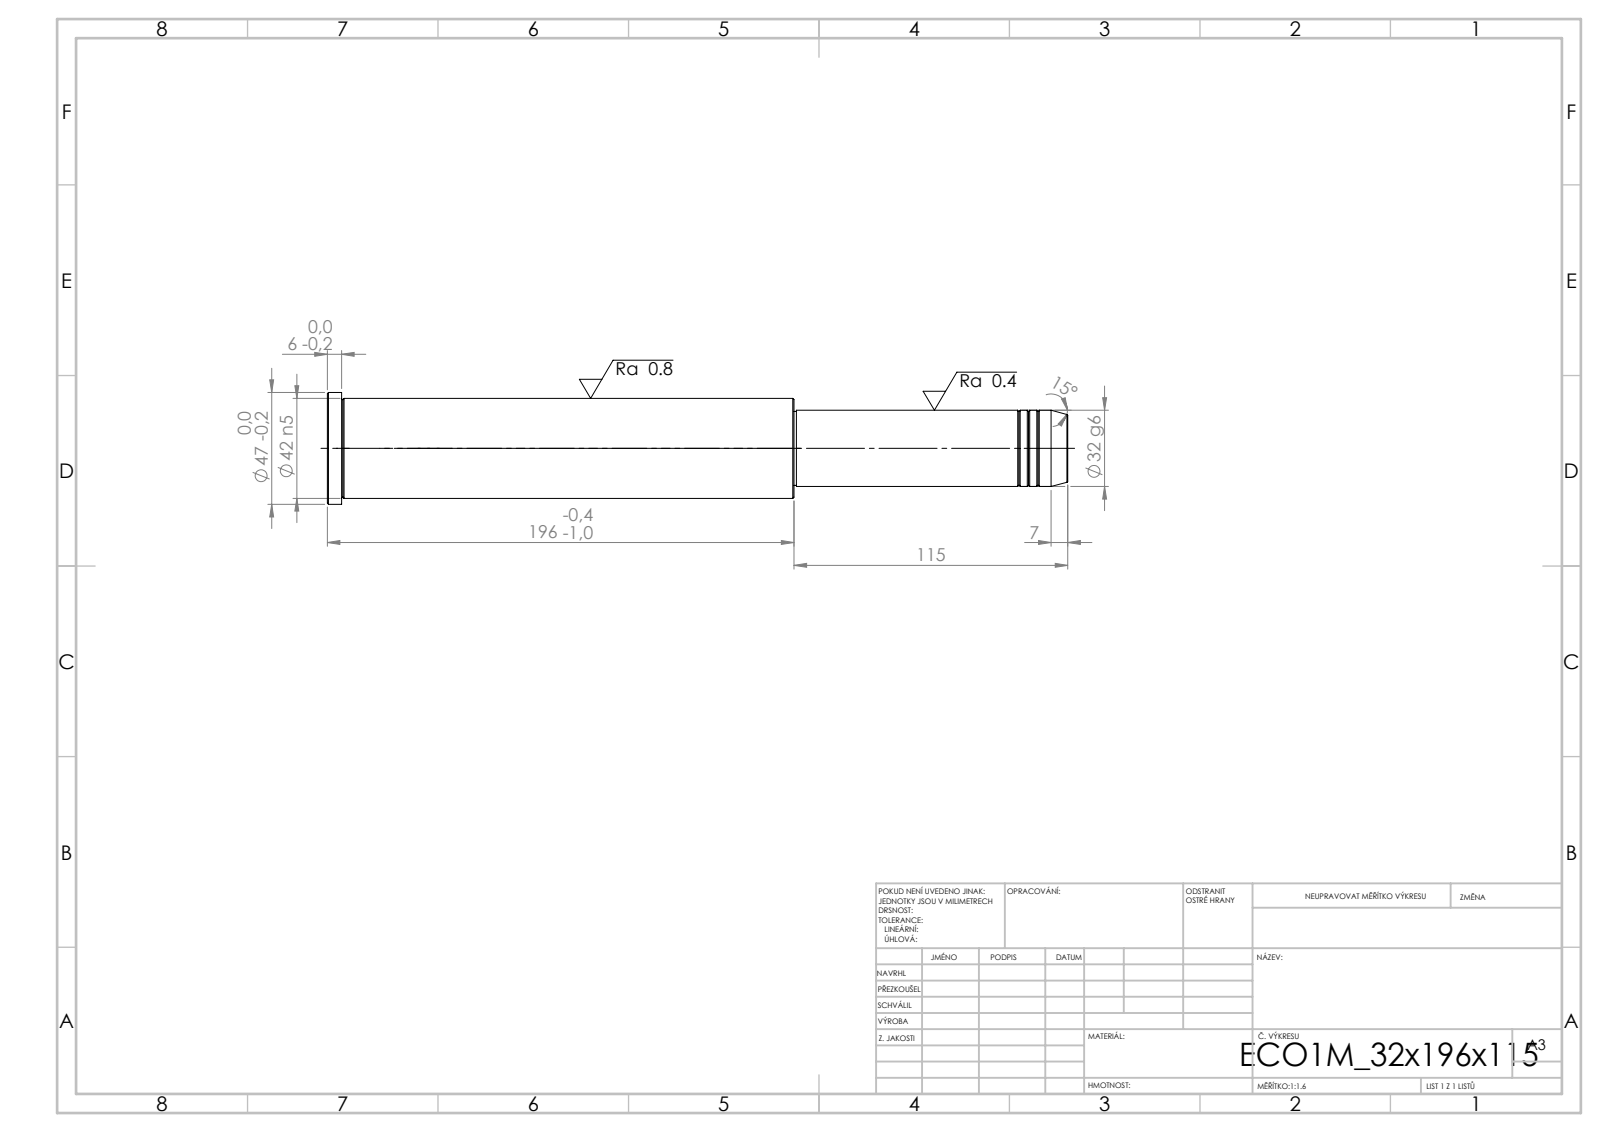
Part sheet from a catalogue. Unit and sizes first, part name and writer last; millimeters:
Units: millimetres
Overall size (bounding box): 311 × 47 × 47
Round bosses / shafts (diameter × count): ⌀47 ×1, ⌀42 ×1, ⌀32 ×1, ⌀31 ×1
Main face-to-face distances: 311, 115, 196, 305, 190, 6, 114, 1, 191, 197
Volume: 365 243 mm³ · Surface area: 41 029 mm²
Bodies: 1 solid, 43 faces (5 planar, 14 cylindrical, 24 other)
STEP written by: SolidWorks 2019 (CONFIG_CONTROL_DESIGN)
